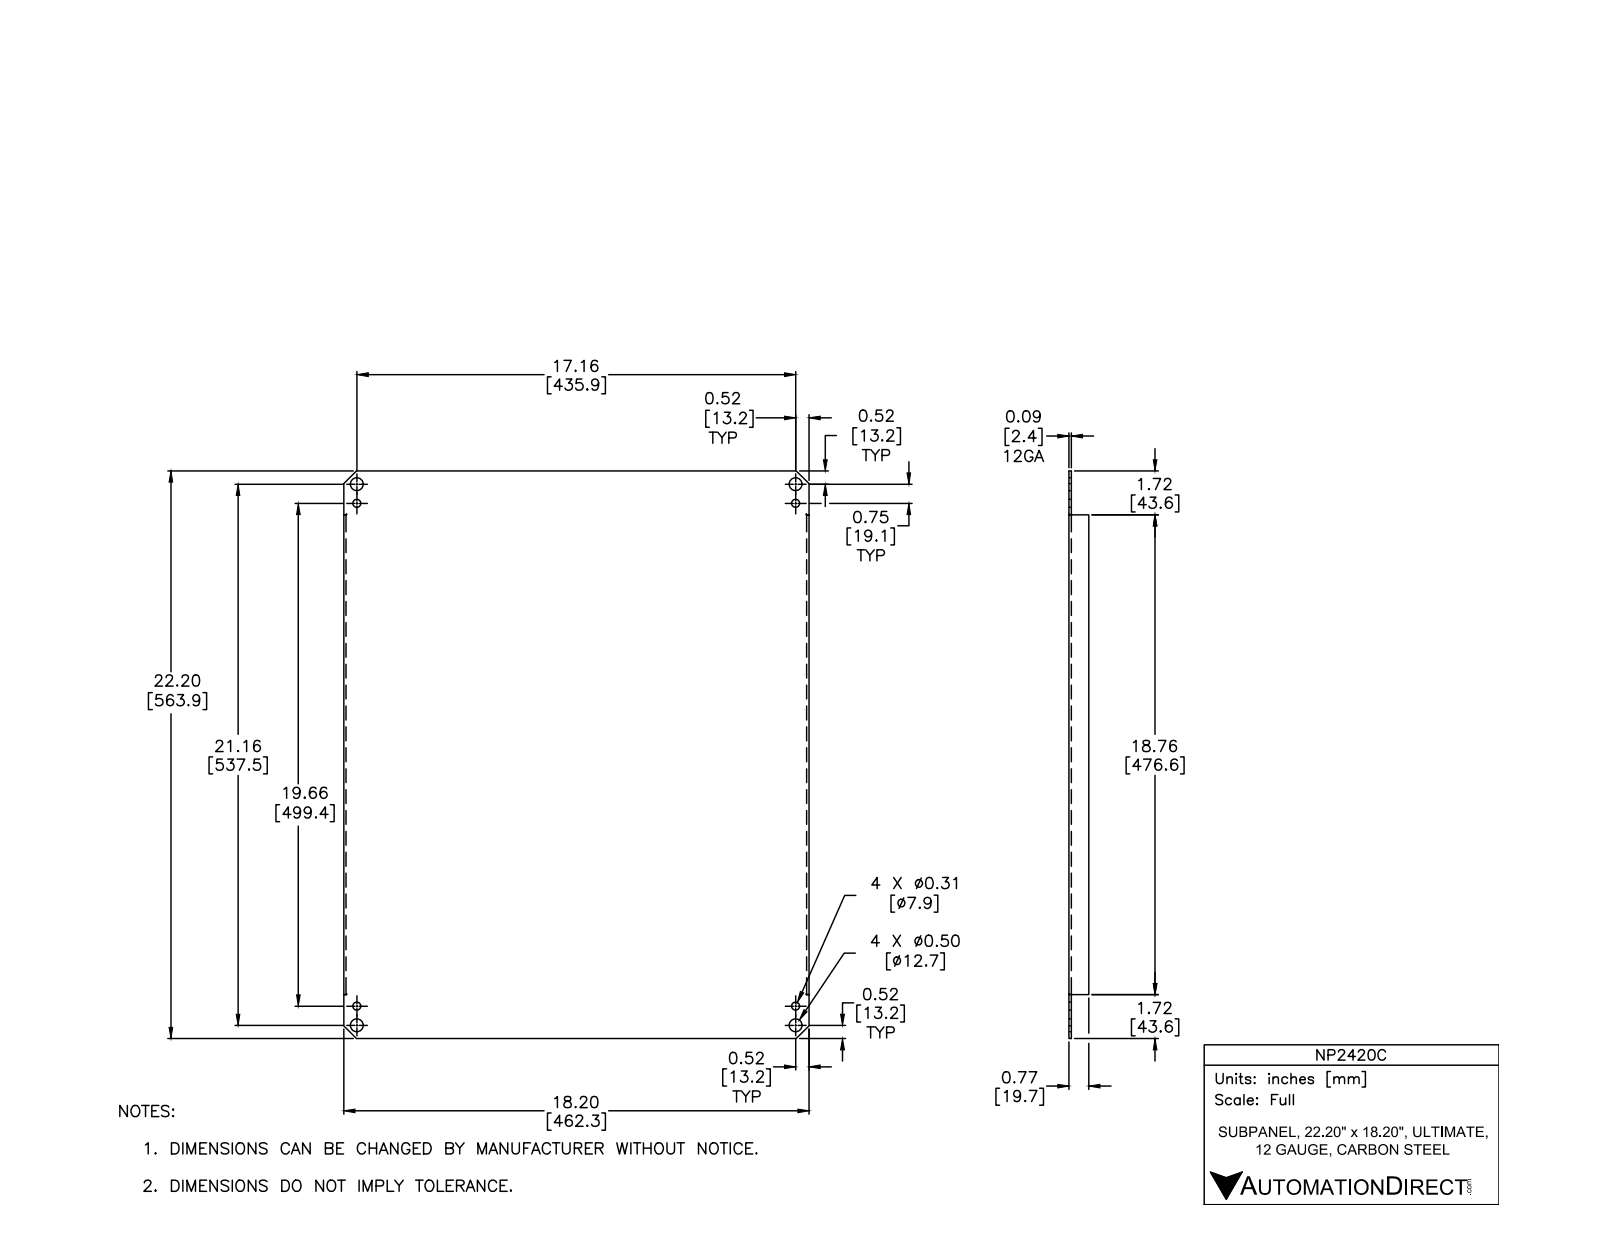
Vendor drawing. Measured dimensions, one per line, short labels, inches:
name: NP2420C
written by: Autodesk Inventor 2012 (AUTOMOTIVE_DESIGN)
unit: in
bodies: 1 solid, 42 faces (30 planar, 12 cylindrical, 0 other)
size: 22.2 × 18.2 × 0.774
volume: 40.03 in³; area: 862.7 in²
holes: 4× ⌀0.313, 4× ⌀0.5
rounds: 2× R0.016, 2× R0.109
face distances: 0.094, 18.106, 18.2, 18.013, 0.68, 0.774, 22.2, 1.718, 20.482, 18.764
hole spacings: 0.75, 17.16, 17.176, 20.41, 26.665, 19.66, 21.16, 26.095
